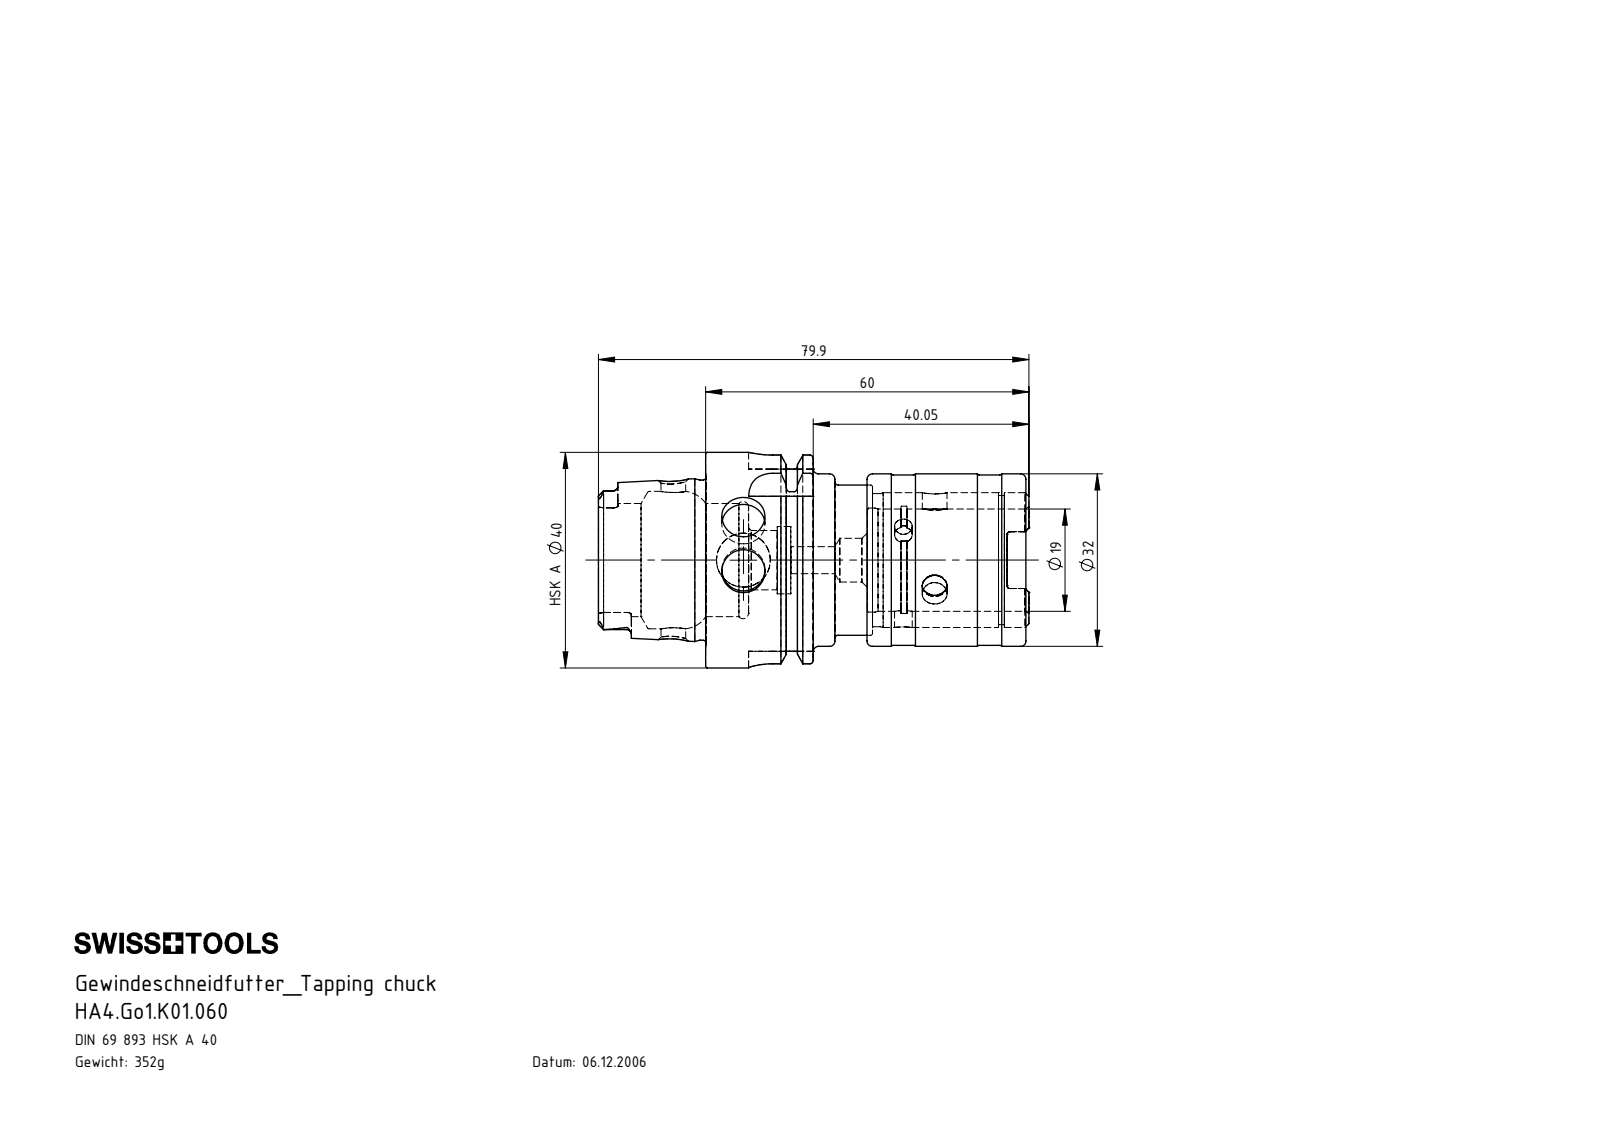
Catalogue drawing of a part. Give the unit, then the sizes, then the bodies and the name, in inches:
Units: inches
Overall size (bounding box): 3.146 × 1.575 × 1.575
Round holes (diameter × count): ⌀0.181 ×4, ⌀0.13 ×3, ⌀0.315 ×3, ⌀0.079 ×1, ⌀0.197 ×1, ⌀0.319 ×1, ⌀0.394 ×1, ⌀0.433 ×1, ⌀0.492 ×1, ⌀0.748 ×1, ⌀0.76 ×1, ⌀0.789 ×1
Round bosses / shafts (diameter × count): ⌀1.575 ×1, ⌀1.368 ×1, ⌀1.26 ×1, ⌀1.244 ×1, ⌀1.17 ×1, ⌀1.096 ×1, ⌀0.984 ×1, ⌀0.972 ×1
Partial cylindrical surfaces — rounded edges, fillets, slot ends (radius × count): R0.035 ×6, R0.074 ×4, R0.177 ×4, R0.085 ×3, R0.02 ×2
Main face-to-face distances: 0.313, 1.219, 0.396, 0.431, 0.868, 1.181, 1.531, 0.433, 0.394, 0.037
Hole centre spacings: 0.228, 1.681, 1.909
Volume: 2.73 in³ · Surface area: 38.22 in²
Bodies: 10 solids, 382 faces (90 planar, 122 cylindrical, 170 other)
Part name (STEP PRODUCT): Kugel Go1; Hülse Go1; Federring innen Go1_gespannt; Federring aussen Go1_gespannt (+6 more)
STEP written by: SolidWorks 2017 (CONFIG_CONTROL_DESIGN)
